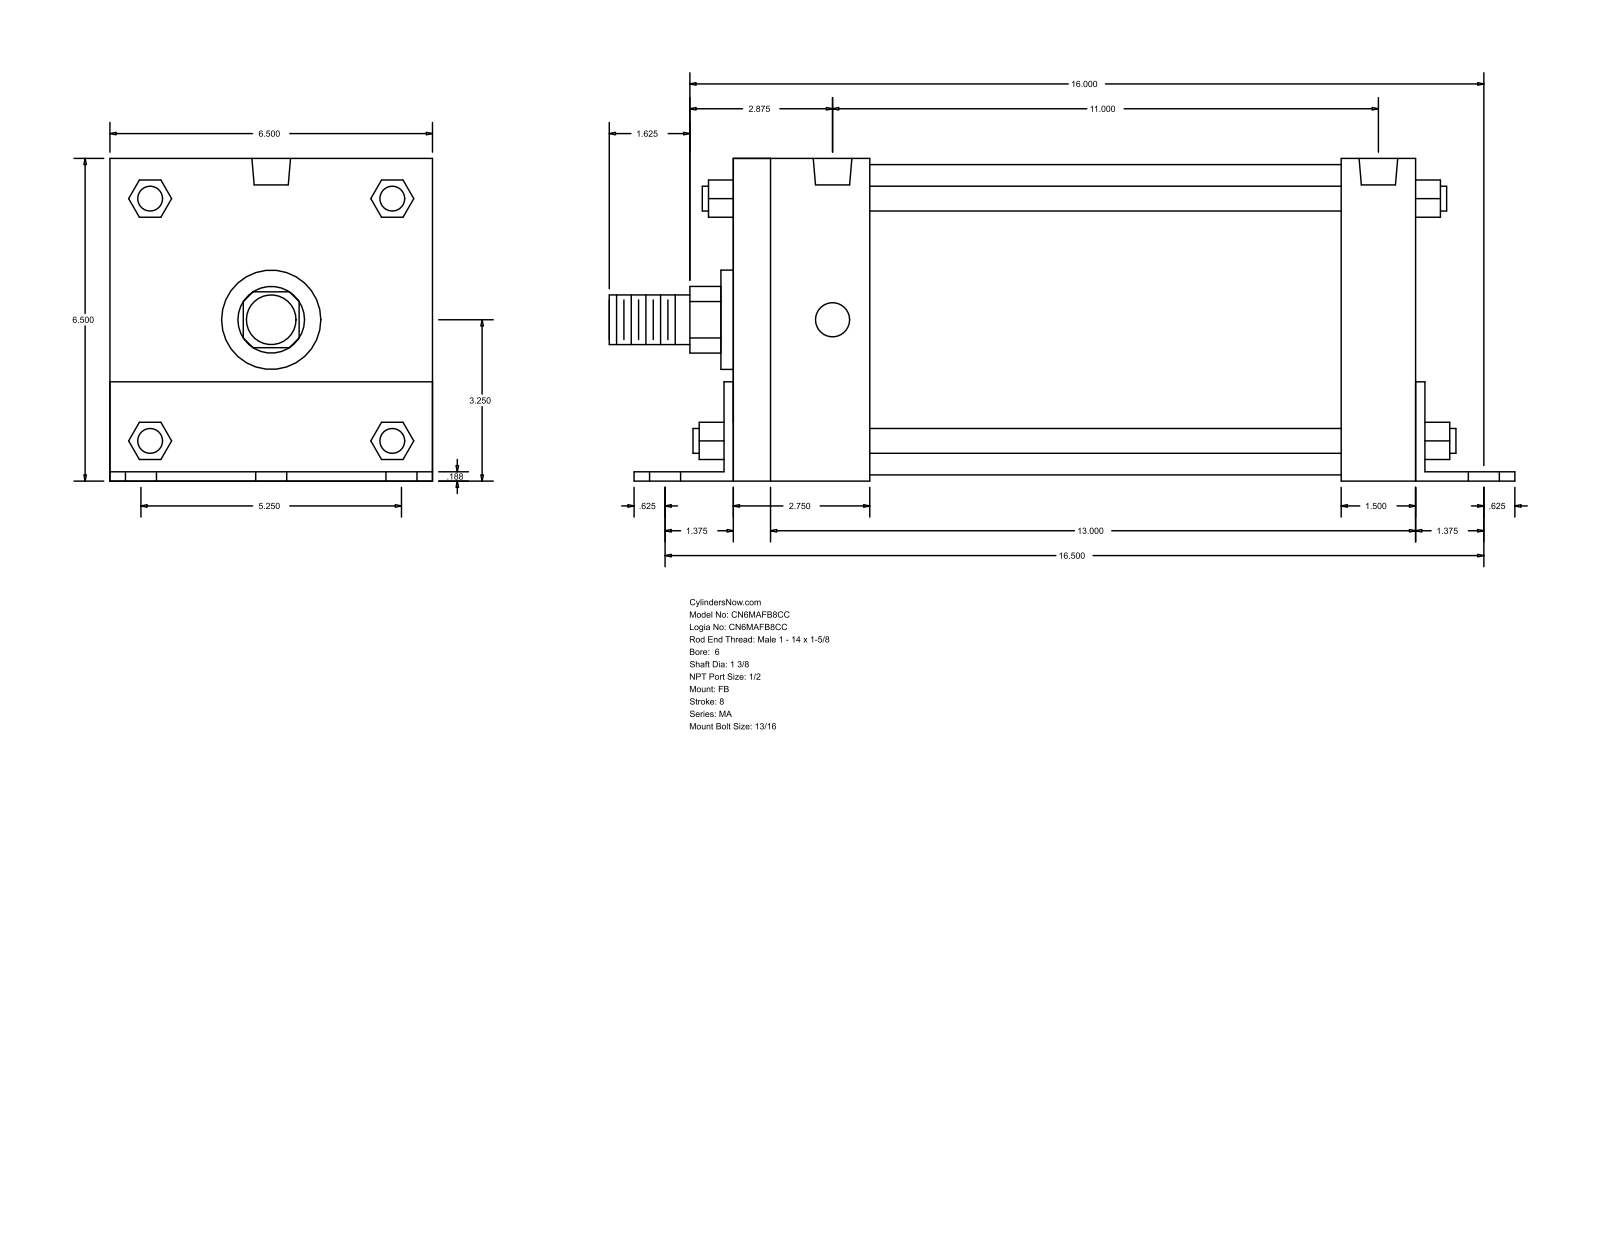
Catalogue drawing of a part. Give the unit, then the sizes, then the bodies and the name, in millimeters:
Units: millimetres
Overall size (bounding box): 460.38 × 165.15 × 165.1
Round holes (diameter × count): ⌀20.64 ×6, ⌀17.46 ×4, ⌀19.77 ×2
Round bosses / shafts (diameter × count): ⌀12.7 ×4, ⌀158.75 ×1, ⌀50.8 ×1, ⌀34.92 ×1, ⌀25.4 ×1
Partial cylindrical surfaces — rounded edges, fillets, slot ends (radius × count): R17.06 ×1, R32.05 ×1
Main face-to-face distances: 165.1, 4.76, 346.07, 165.15, 4.71, 160.39, 4.77, 38.1, 42.86, 355.6
Hole centre spacings: 66.67, 421.24, 415.93, 83.82, 85.78, 108.6, 133.34, 276.22
Bodies: 0 solids, 140 faces (105 planar, 35 cylindrical, 0 other)
Part name (STEP PRODUCT): MA_FB__0600_1.375
STEP written by: GSSL Pune (CONFIG_CONTROL_DESIGN)
